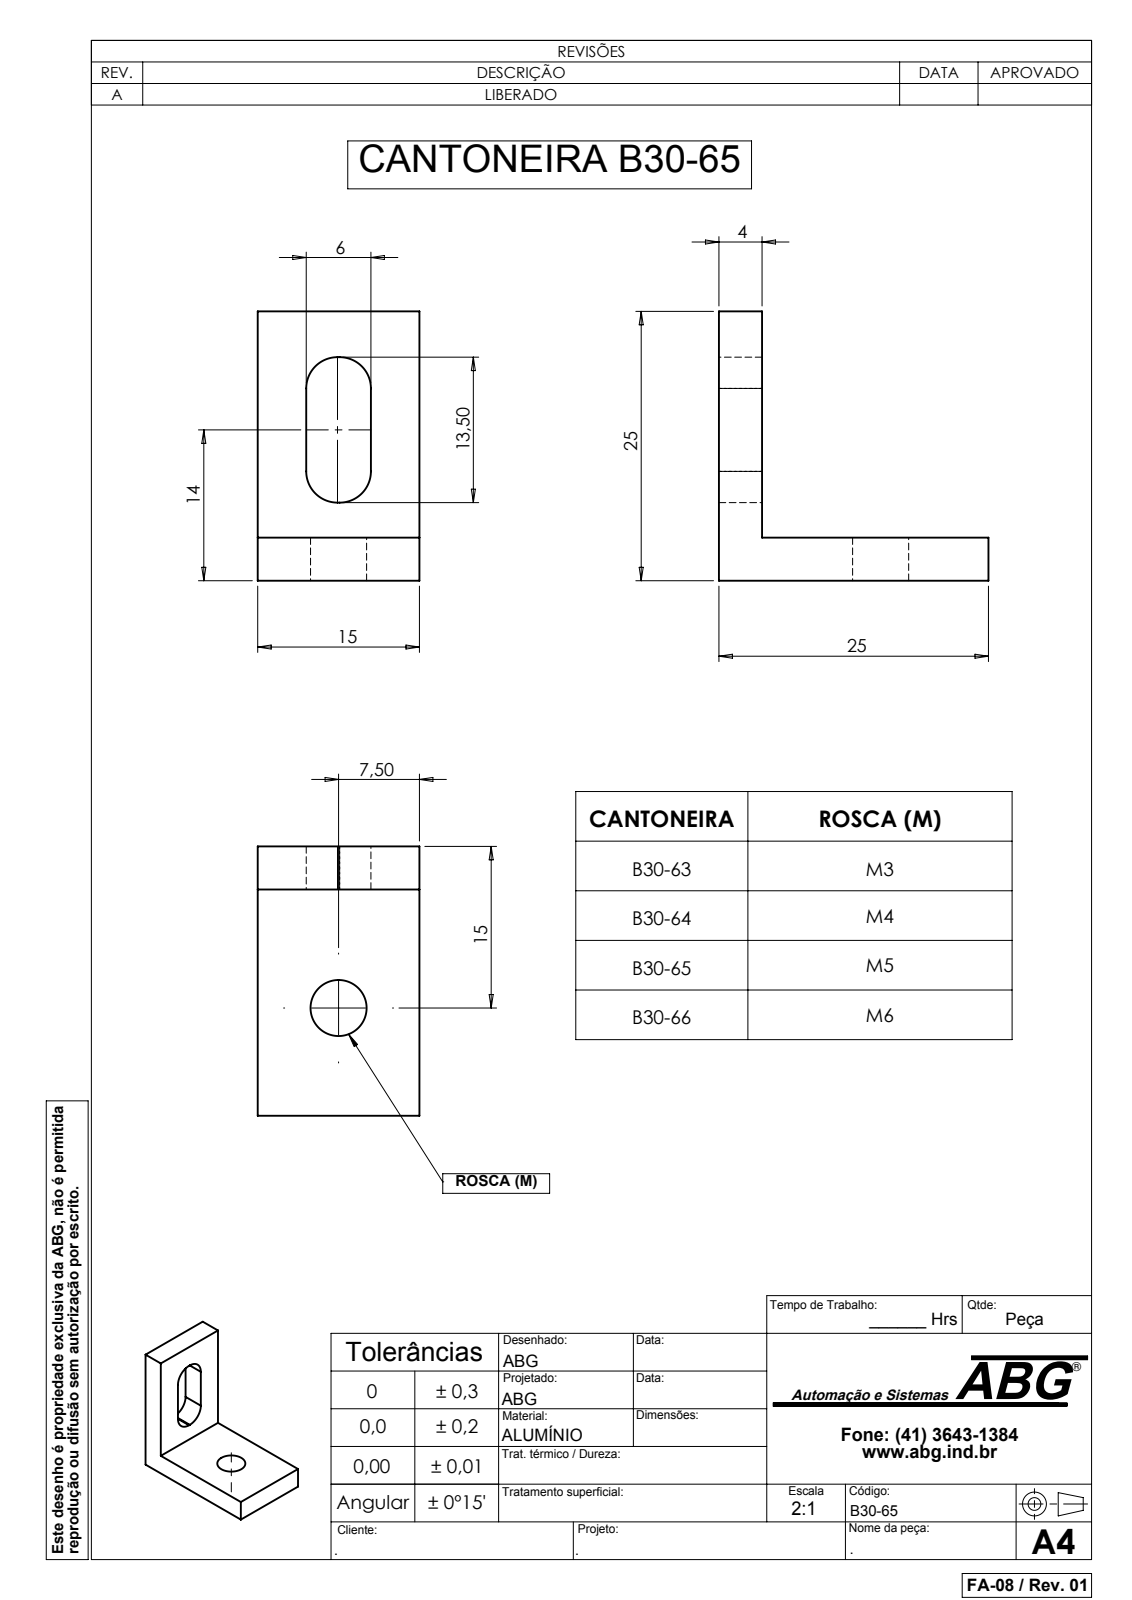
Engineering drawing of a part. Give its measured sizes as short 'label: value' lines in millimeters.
name: B30-64
written by: SolidWorks 2007 (CONFIG_CONTROL_DESIGN)
unit: mm
bodies: 1 solid, 18 faces (12 planar, 6 cylindrical, 0 other)
size: 25 × 25 × 15
volume: 2 415 mm³; area: 1 882 mm²
holes: 1× ⌀4
rounds: 4× R2.9
face distances: 4, 15, 25, 21, 4.5, 10.5, 6, 7.25, 20.75, 3.25
